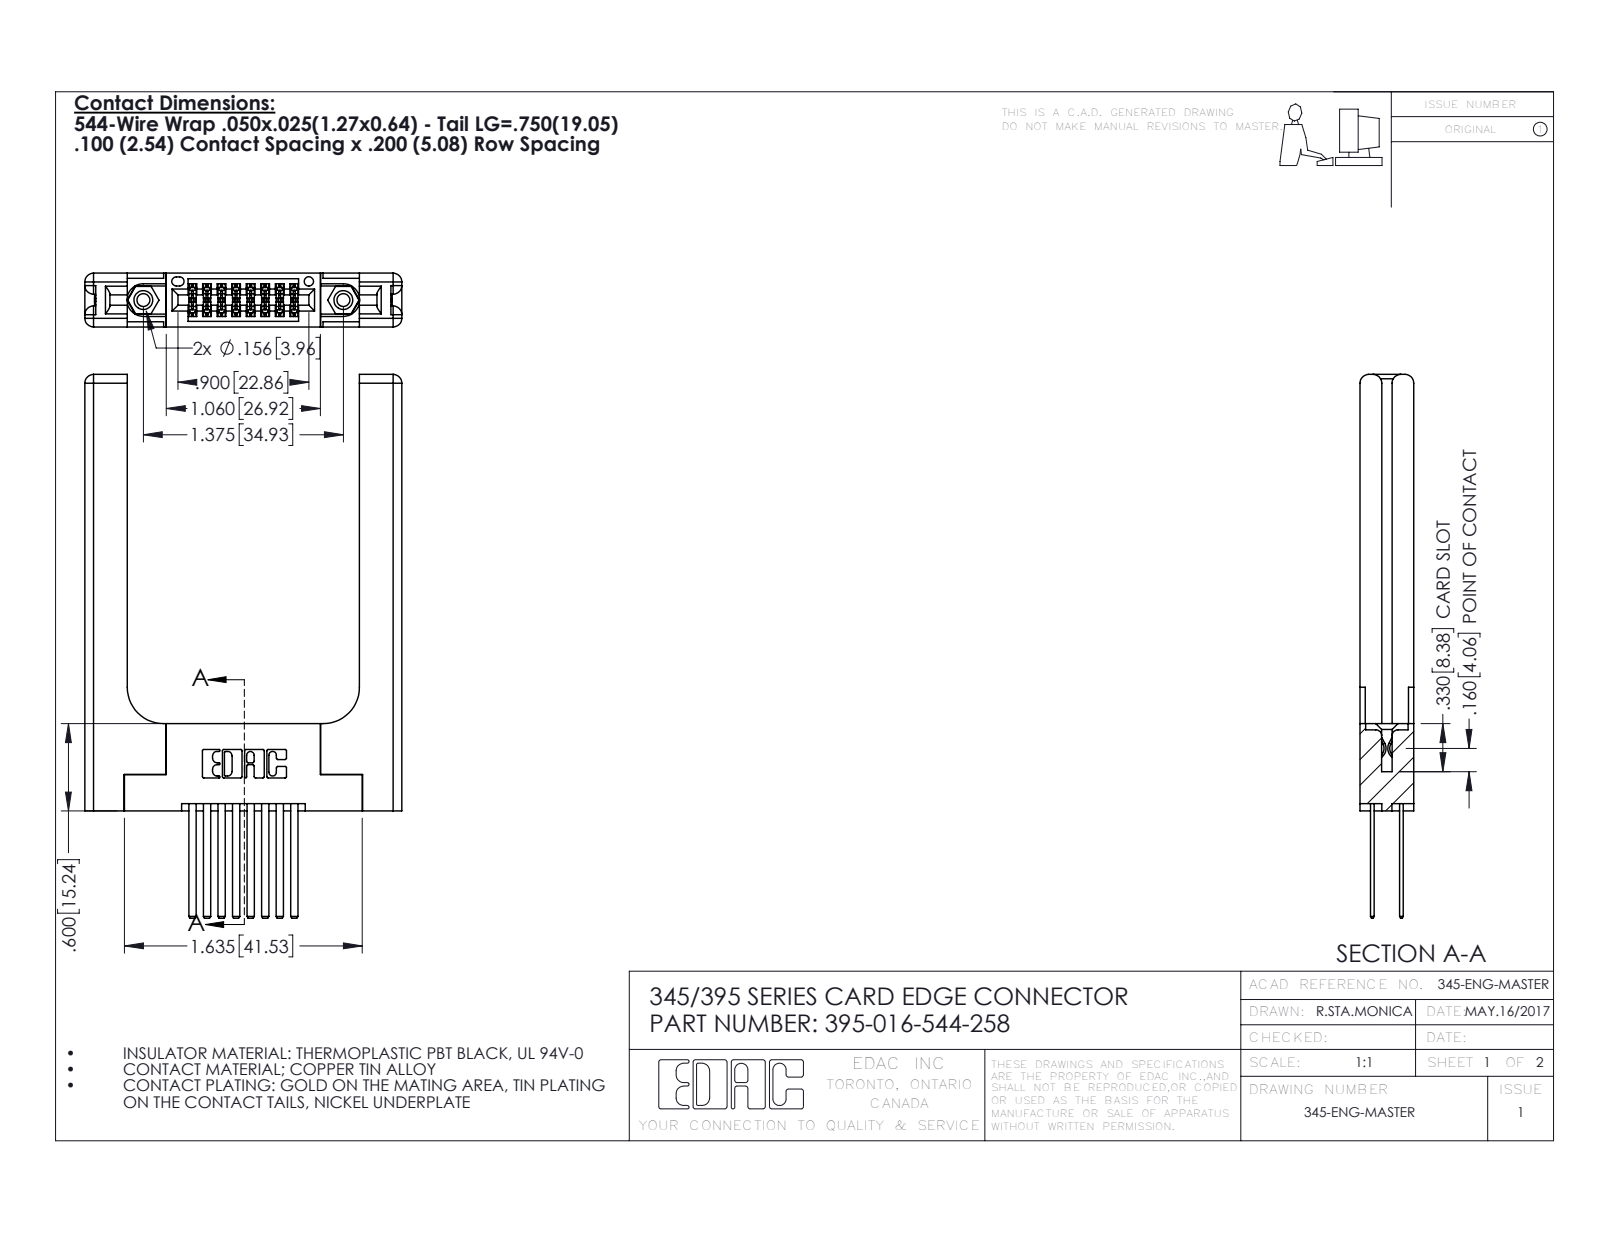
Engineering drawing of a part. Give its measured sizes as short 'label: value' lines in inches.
name: 345-250-001_345-250-001-102; 345 Part_Flush Mounting Lugs - 0.156 Dia-TH; 345-220-058_345-220-058; 345-292-001_345-293-144 (+1 more)
written by: SolidWorks 2016 (CONFIG_CONTROL_DESIGN)
unit: in
bodies: 21 solids, 1086 faces (692 planar, 334 cylindrical, 60 other)
size: 3.737 × 2.179 × 0.37
volume: 0.84 in³; area: 19.95 in²
holes: 2× ⌀0.089, 2× ⌀0.125, 2× ⌀0.156, 1× ⌀0.064
bosses: 2× ⌀0.155
rounds: 24× R0.006, 22× R0.01, 16× R0.06, 6× R0.007, 6× R0.031, 3× R0.026, 2× R0.014, 2× R0.019
face distances: 0.37, 0.072, 0.298, 0.2, 0.077, 0.148, 0.15, 0.22, 0.098, 0.272
hole spacings: 0.27, 1.144, 1.375
